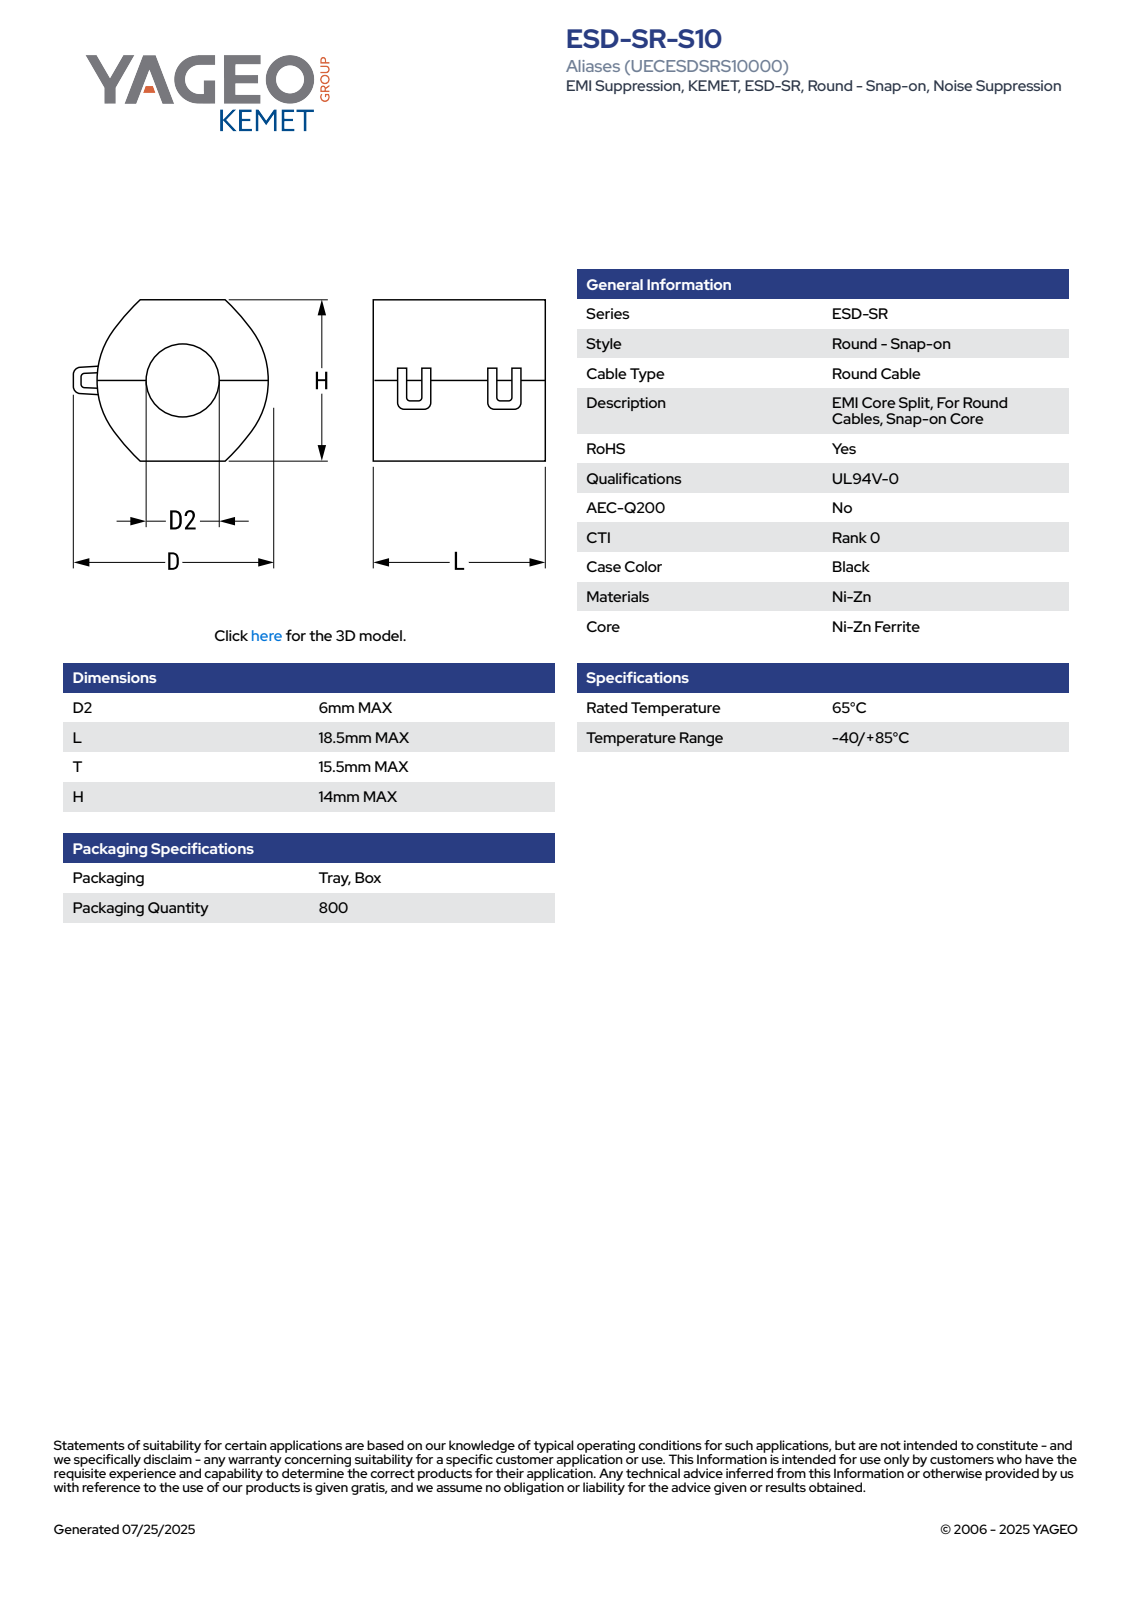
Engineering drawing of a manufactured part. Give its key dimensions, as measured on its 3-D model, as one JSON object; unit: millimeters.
{"part_name": "EC_ESDSRS_D26L18.5T15.5H14", "step_written_by": "SolidWorks 2014 (AUTOMOTIVE_DESIGN)", "units": "millimeters", "bodies": {"solids": 2, "faces": 84, "planar": 78, "cylindrical": 6, "other": 0}, "overall_size": [18.5, 15.5, 14], "volume_mm3": 2684, "surface_area_mm2": 1871, "round_holes": [[6, 1]], "partial_cylinders_radius": [[7.5, 1]], "face_to_face_distances": [6.99, 7.01, 18.5, 14, 0.53, 3.37, 7.37, 11.13, 15.13, 4]}
